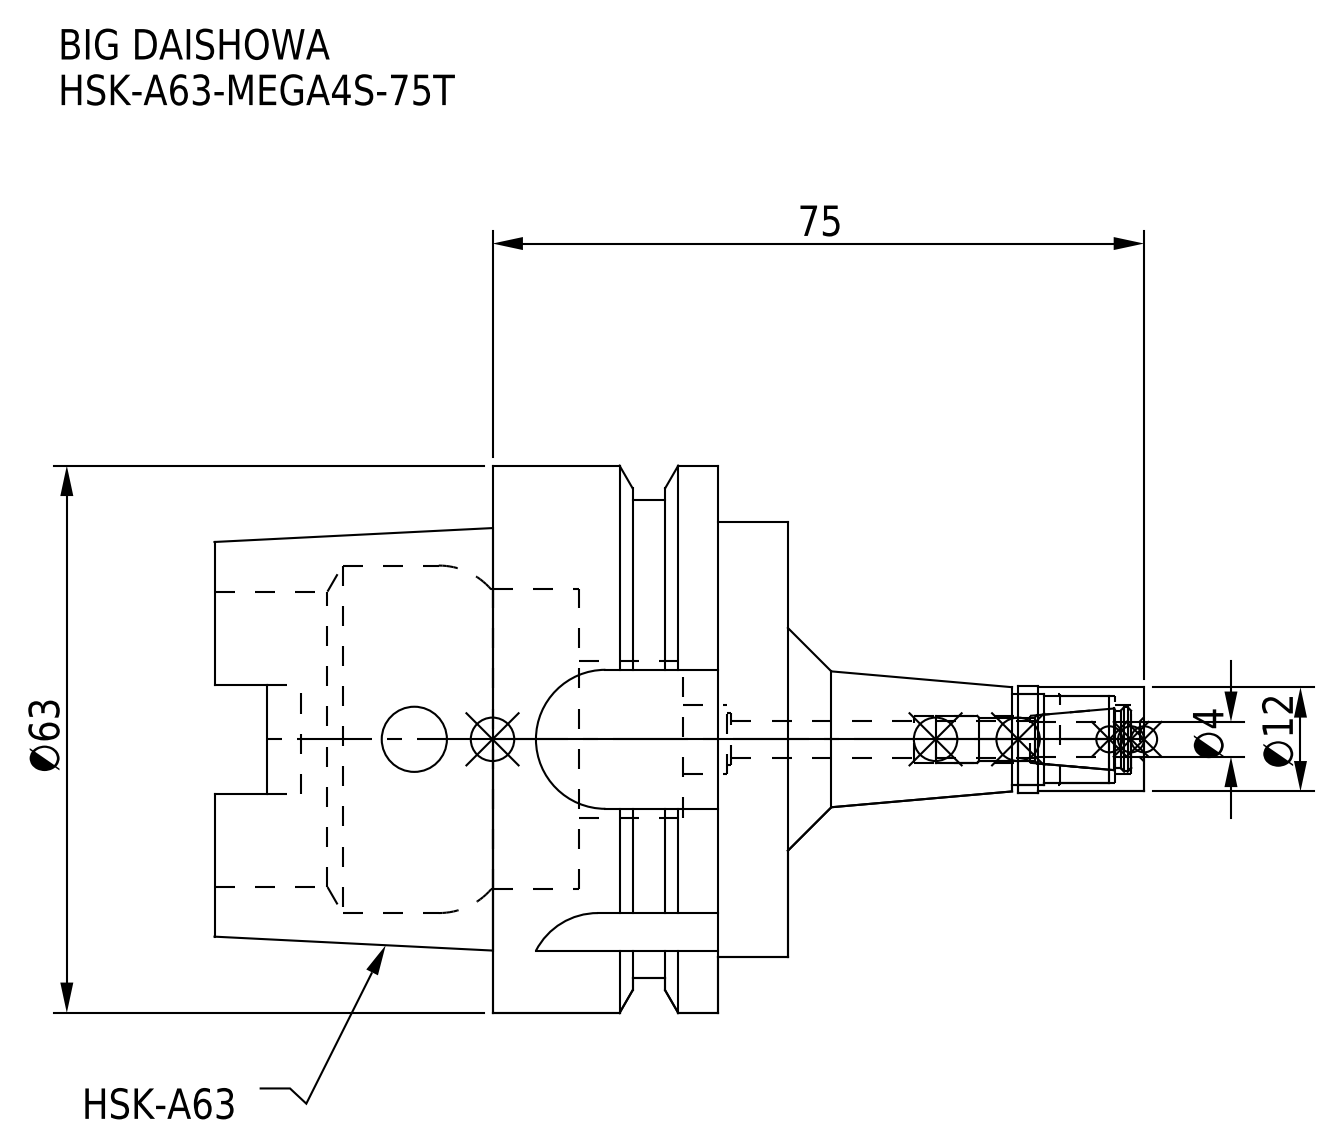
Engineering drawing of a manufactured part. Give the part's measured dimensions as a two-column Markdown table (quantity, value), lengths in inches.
| quantity | value |
| --- | --- |
| part name | HA63MS04075T-040_ASM.stp; HSK-A63-MEGA4S-75T; HSK-A63-MEGA4S-75T-040.stp; DXF_TEMP_ASSY_ASM_4_ASM.stp (+3 more) |
| STEP written by | SolidWorks 2019 (CONFIG_CONTROL_DESIGN) |
| units | inches |
| bodies | 2 solids, 125 faces (48 planar, 55 cylindrical, 22 other) |
| overall size | 4.213 × 2.48 × 2.48 |
| volume | 6.272 in³ |
| surface area | 41.62 in² |
| round holes (diameter × count) | 0.161 × 1, 0.165 × 1, 0.213 × 1, 0.236 × 1, 0.295 × 1, 0.315 × 1, 0.394 × 1, 0.413 × 1, 0.709 × 1, 1.339 × 1, 1.358 × 1, 1.575 × 1 |
| round bosses / shafts (diameter × count) | 2.48 × 1, 2.165 × 1, 1.969 × 1, 0.484 × 1, 0.472 × 1 |
| partial cylindrical surfaces (radius × count) | 0.113 × 4, 0.315 × 4 |
| main face-to-face distances | 1.339, 1.024, 0.315, 0.947, 0.632, 0.392, 2.598, 2.283, 1.652, 1.26 |
